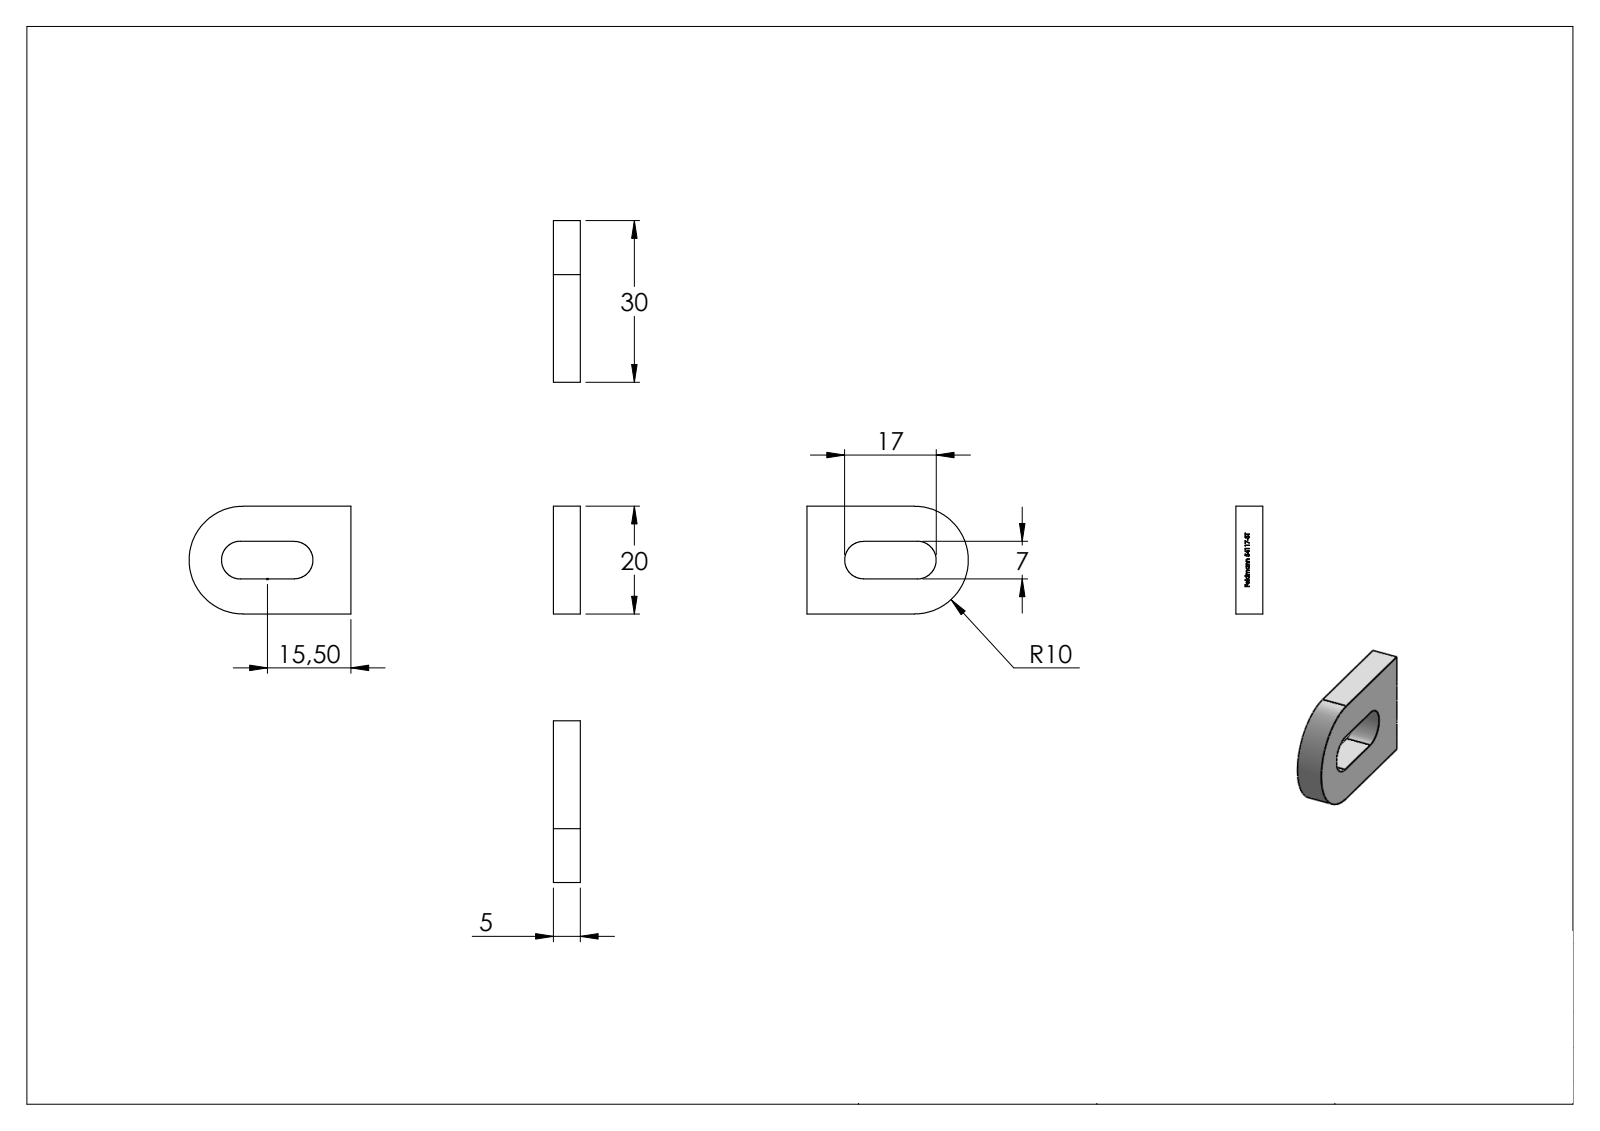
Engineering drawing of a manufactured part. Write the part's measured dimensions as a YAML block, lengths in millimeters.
part_name: "54117-ST"
step_written_by: "SolidWorks 2015 (CONFIG_CONTROL_DESIGN)"
units: millimeters
bodies: {solids: 1, faces: 208, planar: 132, cylindrical: 5, other: 71}
overall_size: [30, 20, 5]
volume: 2243
surface_area: 1569
partial_cylinders:
  - {radius: 3.5, count: 2}
  - {radius: 10, count: 1}
face_to_face_distances: [5, 6.5, 13.5, 20, 7, 3.29, 2.5, 1.79, 0.61, 1.71]
